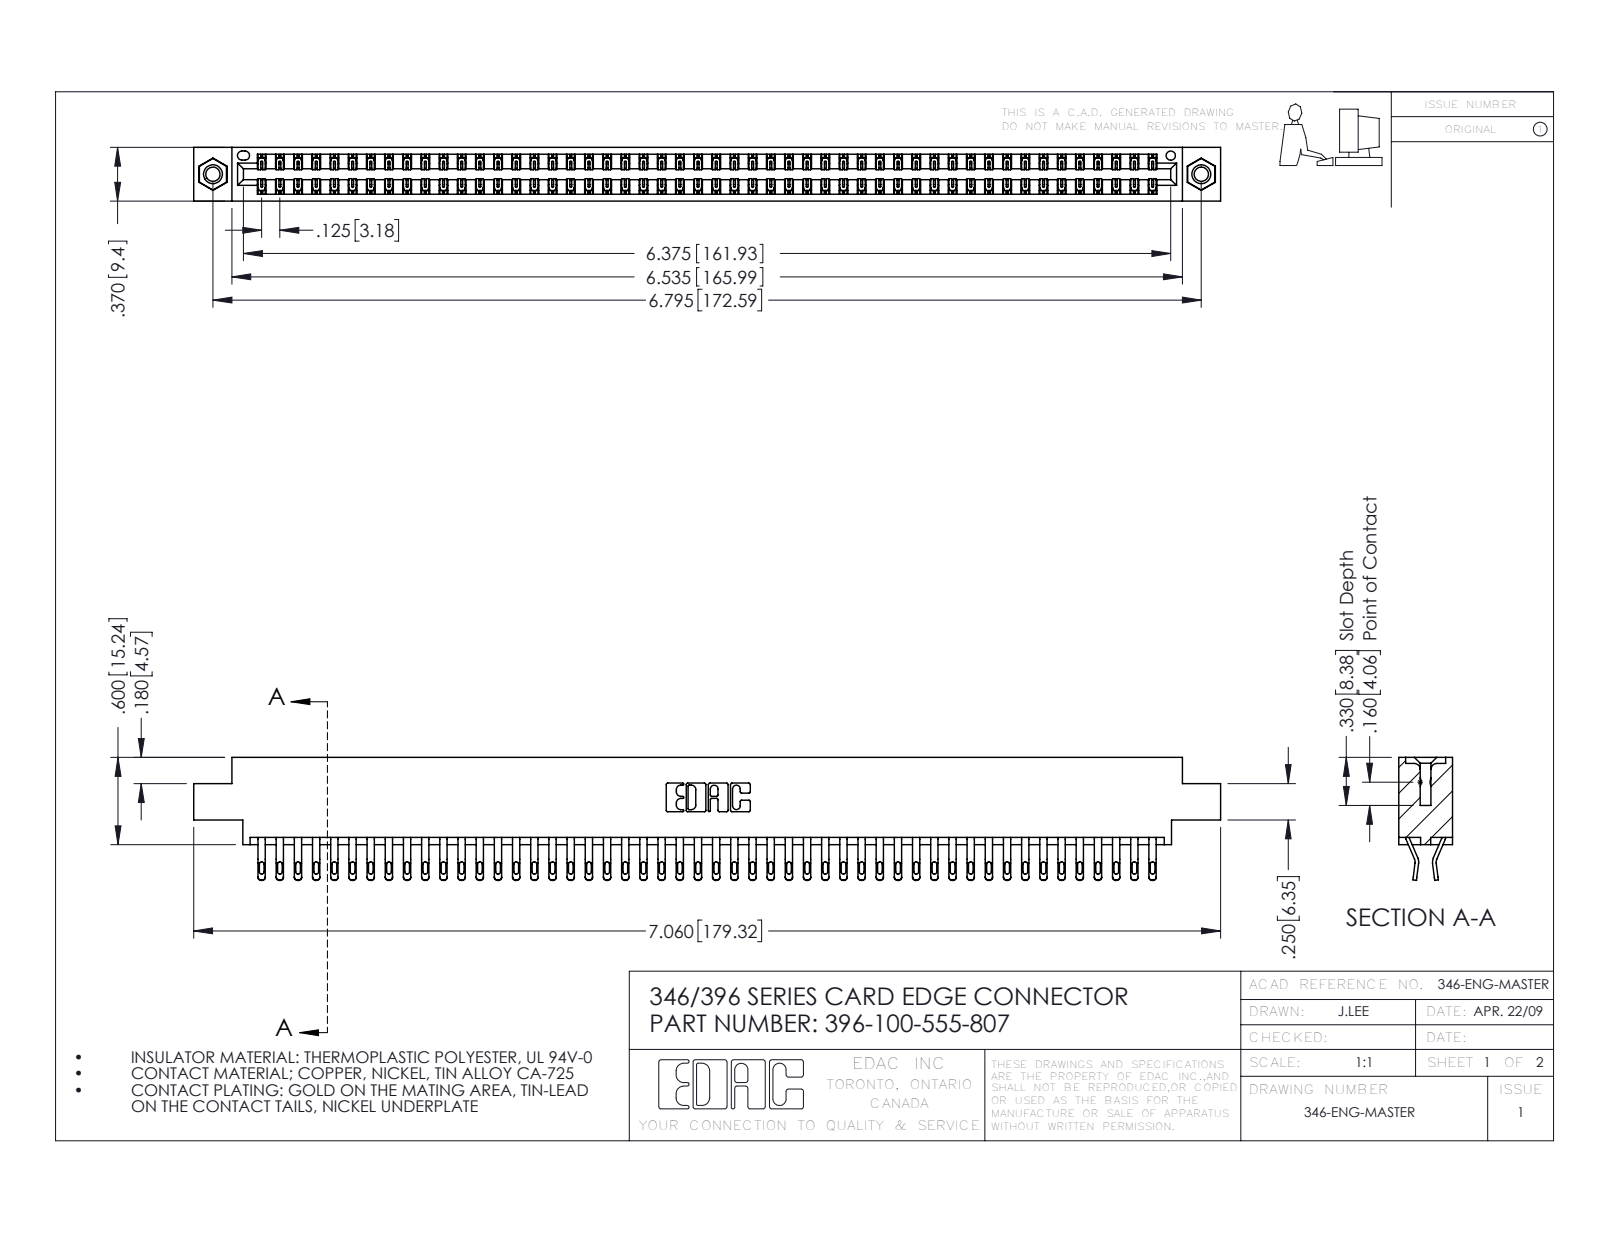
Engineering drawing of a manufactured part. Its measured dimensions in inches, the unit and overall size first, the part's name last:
Units: inches
Overall size (bounding box): 7.06 × 0.845 × 0.37
Round holes (diameter × count): ⌀0.098 ×2, ⌀0.125 ×2, ⌀0.156 ×2, ⌀0.064 ×1
Round bosses / shafts (diameter × count): ⌀0.155 ×2
Partial cylindrical surfaces — rounded edges, fillets, slot ends (radius × count): R0.016 ×200, R0.02 ×200, R0.006 ×150, R0.01 ×22, R0.007 ×6, R0.031 ×6, R0.026 ×3, R0.01 ×2
Main face-to-face distances: 0.048, 0.322, 0.37, 0.25, 0.025, 0.072, 0.298, 0.275, 0.222, 0.148
Hole centre spacings: 0.246, 6.586, 6.795
Volume: 1.078 in³ · Surface area: 39.78 in²
Bodies: 103 solids, 5986 faces (3412 planar, 2558 cylindrical, 16 other)
Part name (STEP PRODUCT): 345-250-001_345-250-005-103; 346 Part_0.170 Offset - 0.156 Dia-TI; 345-292-001_555 Tail; 396-100-555-807
STEP written by: SolidWorks 2016 (CONFIG_CONTROL_DESIGN)
